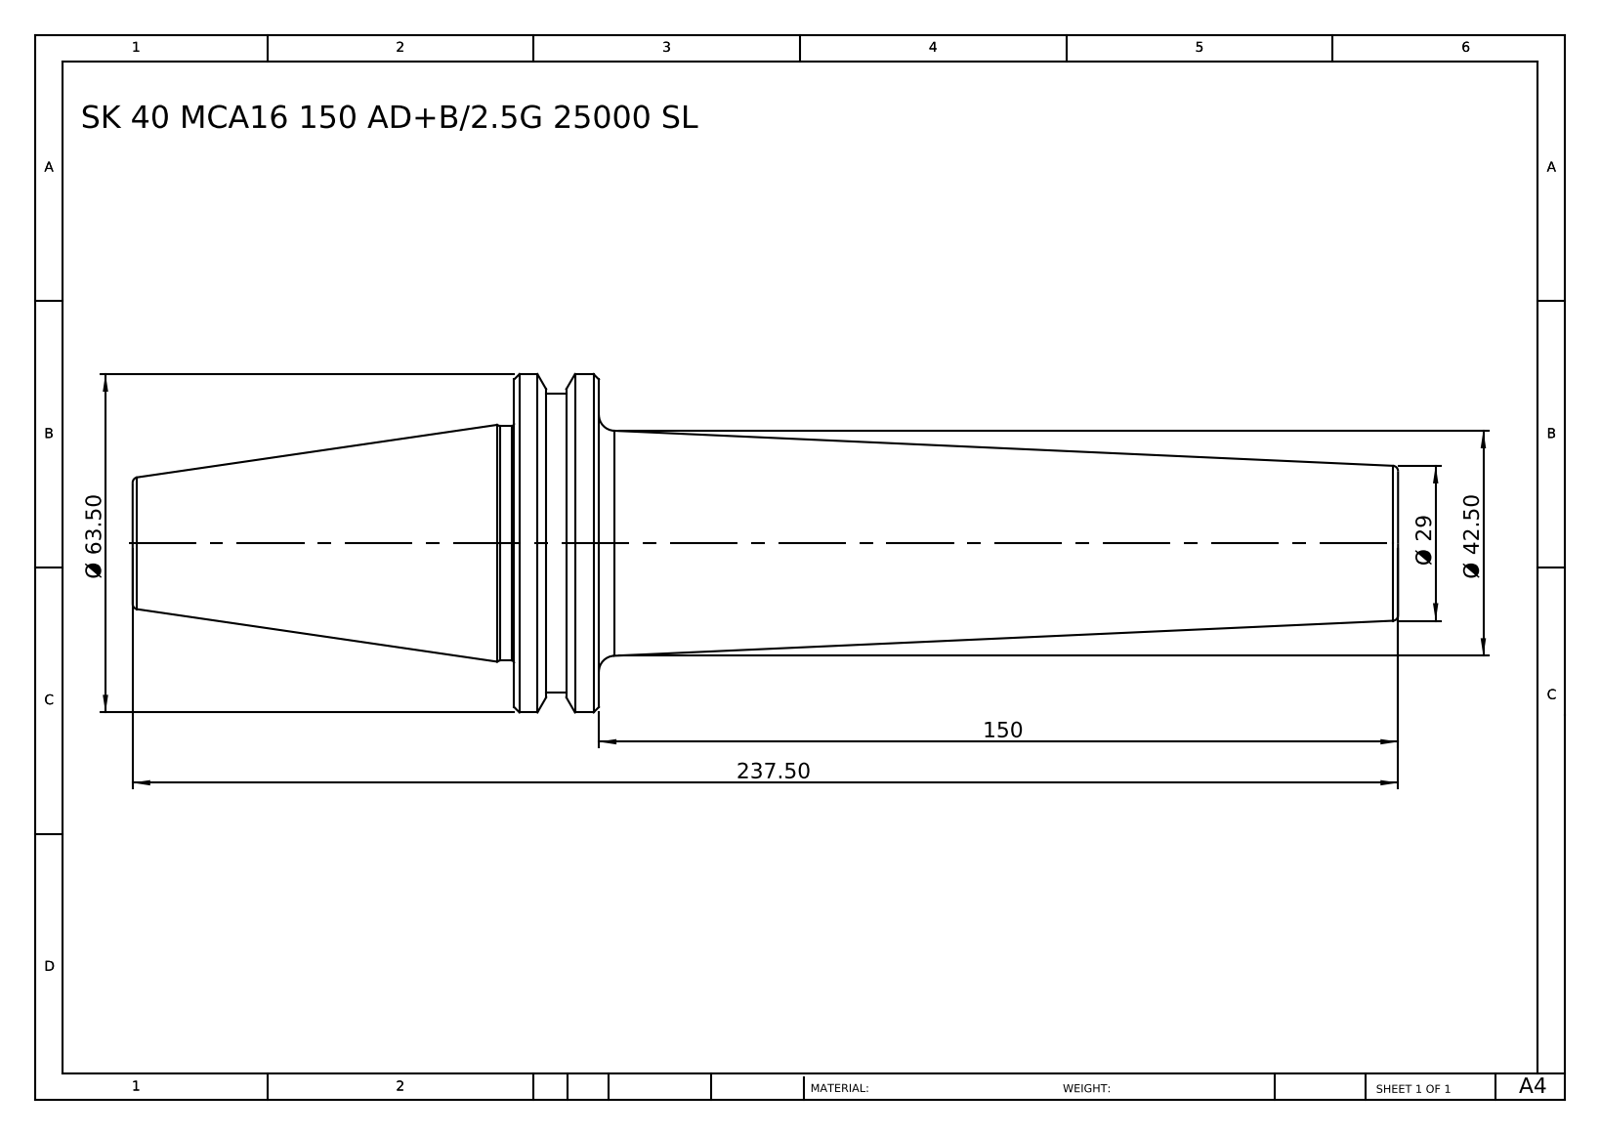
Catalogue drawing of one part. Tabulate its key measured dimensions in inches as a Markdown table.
| quantity | value |
| --- | --- |
| part name | SK 40 MCA16 150 AD+B-2.5G 25000 SL |
| STEP written by | SolidWorks 2014 (CONFIG_CONTROL_DESIGN) |
| units | inches |
| bodies | 1 solid, 38 faces (6 planar, 8 cylindrical, 24 other) |
| overall size | 9.35 × 2.5 × 2.5 |
| volume | 16.46 in³ |
| surface area | 50.93 in² |
| round bosses / shafts (diameter × count) | 2.5 × 1, 2.205 × 1, 1.732 × 1 |
| main face-to-face distances | 0.626, 5.906, 6.531, 9.35, 3.445, 2.819, 6.295, 0.39, 0.236, 3.055 |
